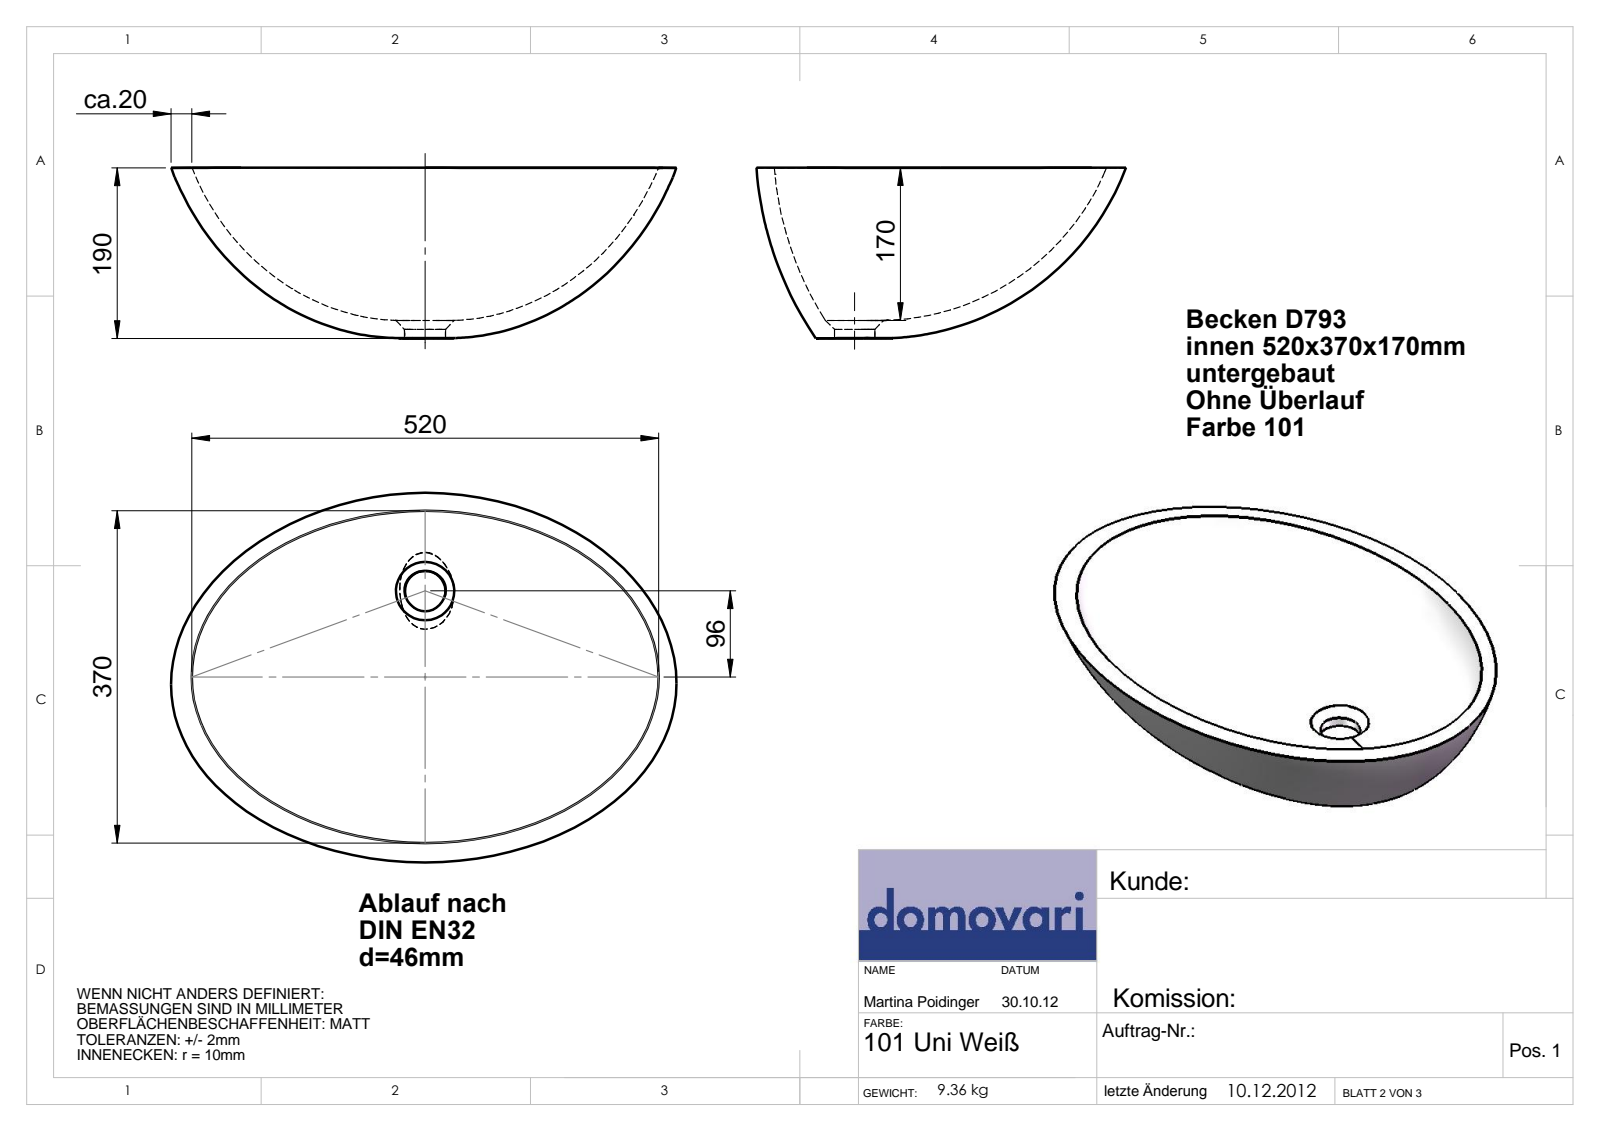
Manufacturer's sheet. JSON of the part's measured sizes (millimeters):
{"part_name": "D793", "step_written_by": "SolidWorks 2017 (AUTOMOTIVE_DESIGN)", "units": "millimeters", "bodies": {"solids": 2, "faces": 32, "planar": 16, "cylindrical": 4, "other": 12}, "overall_size": [560.88, 411.63, 195], "volume_mm3": 5480000, "surface_area_mm2": 652674, "partial_cylinders_radius": [[23, 1]], "face_to_face_distances": [10, 380, 530, 390, 370, 185, 195, 540, 520, 5]}
